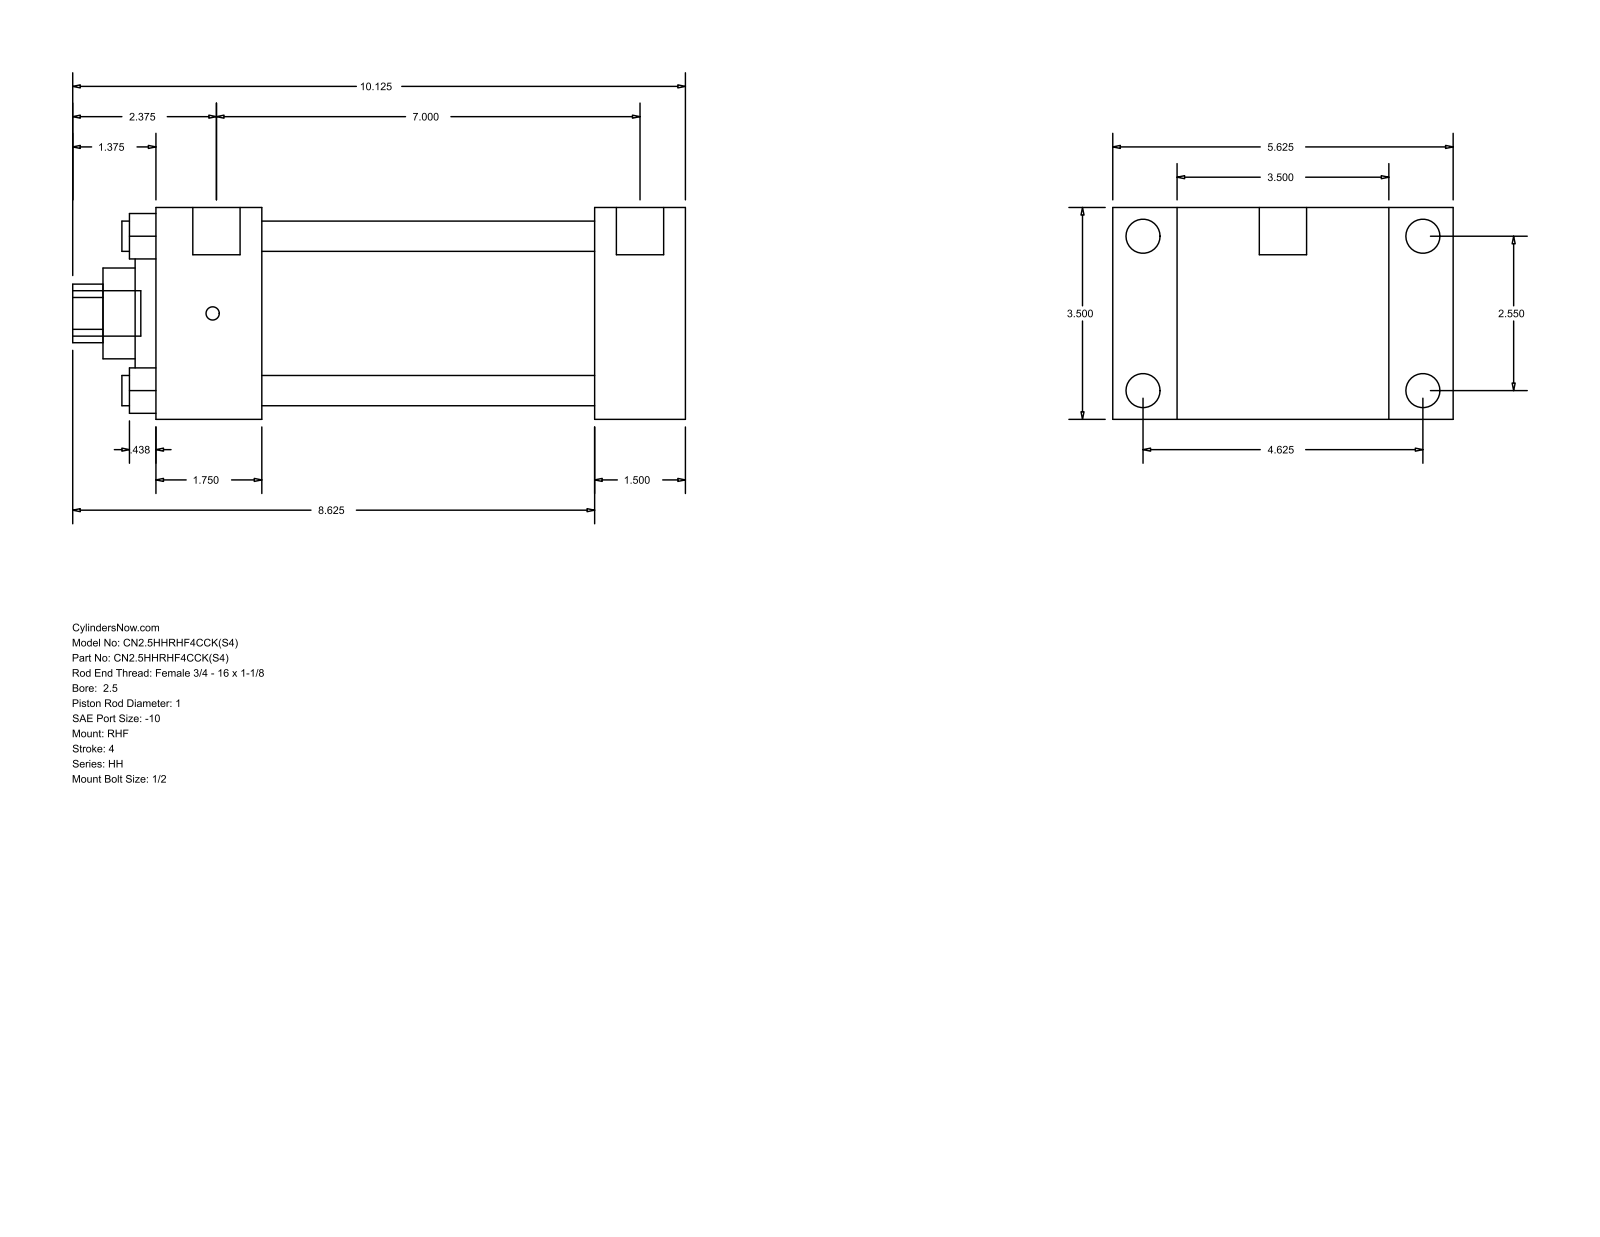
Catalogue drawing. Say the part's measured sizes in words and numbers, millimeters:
The part is named "HH_RHF__0250_1". Its 3-D file was written by "GSSL Pune (CONFIG_CONTROL_DESIGN)". It is 0 solids with 90 faces: 61 planar, 29 cylindrical and 0 other. Overall it measures 257.18 by 142.88 by 88.9 millimeters. Round holes: 4 of diameter 12.7, 1 of diameter 25.4, 1 of diameter 38.1, 1 of diameter 60.33, 1 of diameter 73.03. Round bosses or shafts: 4 of diameter 14.3, 4 of diameter 5.56, 2 of diameter 19.84, 1 of diameter 19.05. Partial cylindrical surfaces (rounded edges, fillets, slot ends): 1 of radius 12.29. The main face-to-face distances are 88.9, 38.11, 26.99, 115.89, 184.15, 222.26, 142.88, 44.46, 139.69, 177.8. The hole center spacings are 45.79, 64.76, 91.58.
